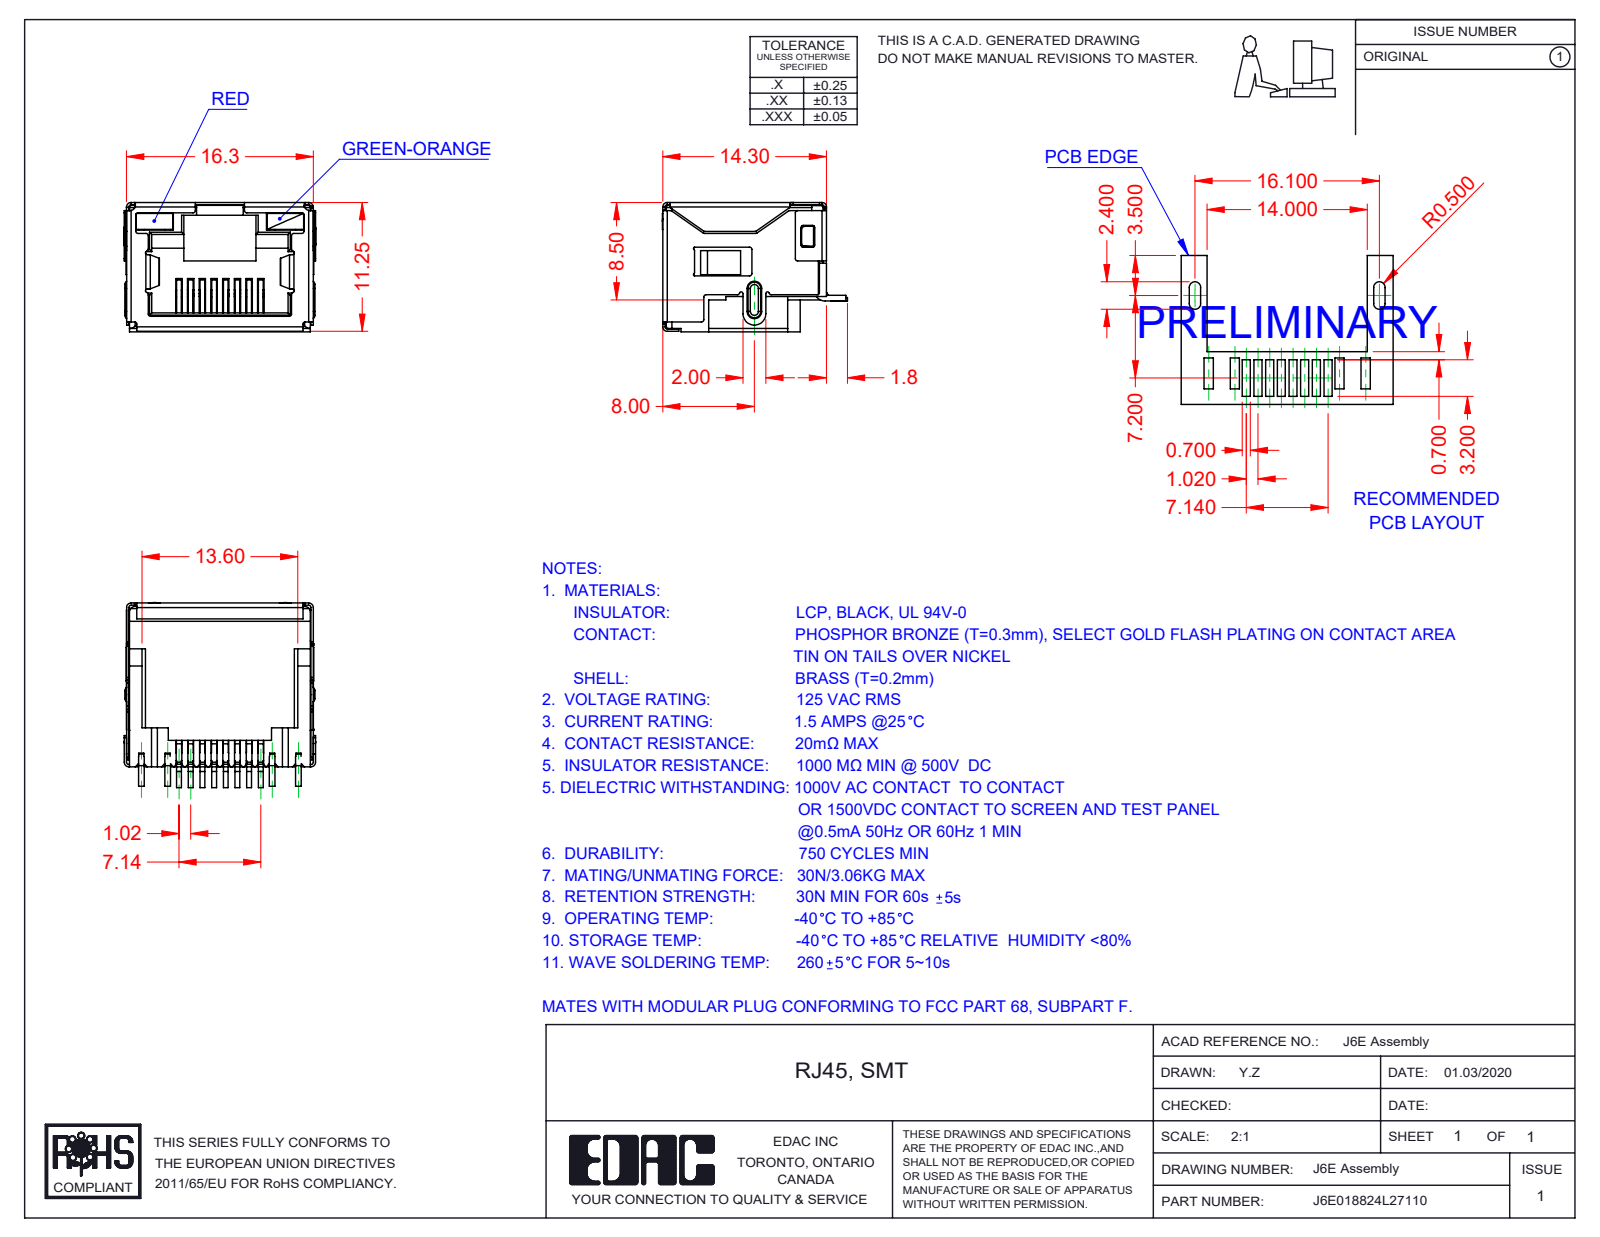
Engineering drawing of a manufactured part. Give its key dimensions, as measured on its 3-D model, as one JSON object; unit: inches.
{"part_name": "6E Contacts; J6E018824L27110; 6E Insulator_LED; 6E LED LH_2-Red (+2 more)", "step_written_by": "SolidWorks 2016 (CONFIG_CONTROL_DESIGN)", "units": "inches", "bodies": {"solids": 12, "faces": 1498, "planar": 1099, "cylindrical": 349, "other": 50}, "overall_size": [0.659, 0.636, 0.445], "volume_in3": 0.068, "surface_area_in2": 6.27, "partial_cylinders_radius": [[0.008, 82], [0.01, 17], [0.016, 13], [0.02, 13], [0.004, 10], [0.006, 7], [0.012, 4], [0.039, 3]], "face_to_face_distances": [0.435, 0.632, 0.634, 0.624, 0.437, 0.445, 0.094, 0.028, 0.388, 0.019]}
